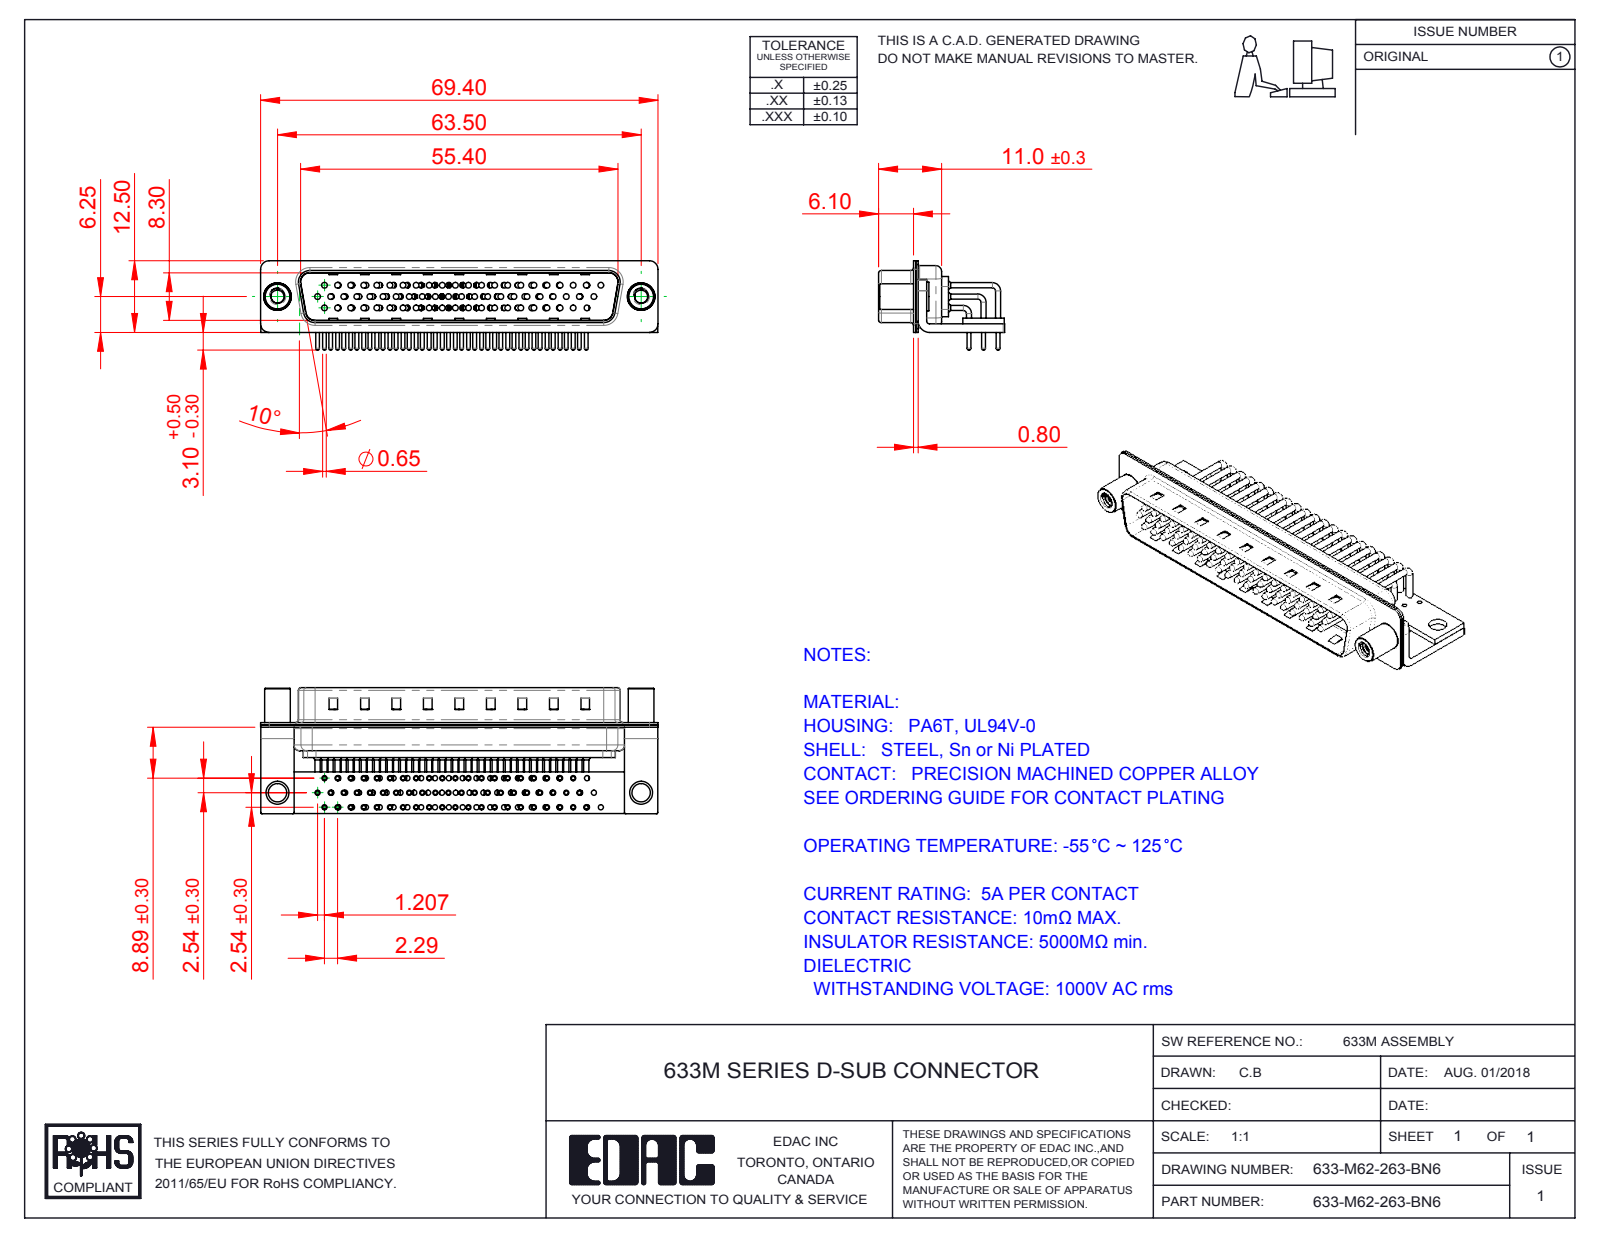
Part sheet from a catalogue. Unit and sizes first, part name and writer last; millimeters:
Units: millimetres
Overall size (bounding box): 69.4 × 22 × 15.6
Round holes (diameter × count): ⌀0.9 ×62, ⌀1 ×62, ⌀1.7 ×62, ⌀2 ×62, ⌀2.26 ×2, ⌀3.2 ×2, ⌀4 ×2, ⌀4.8 ×2
Round bosses / shafts (diameter × count): ⌀0.9 ×118, ⌀1.5 ×62, ⌀0.65 ×62, ⌀1 ×56, ⌀5 ×2, ⌀4.9 ×2, ⌀4.5 ×2
Partial cylindrical surfaces — rounded edges, fillets, slot ends (radius × count): R1.01 ×62, R0.25 ×16, R1.5 ×16, R2 ×13, R0.5 ×9, R1.6 ×8, R0.6 ×4, R0.65 ×4
Main face-to-face distances: 0.4, 0.85, 1.25, 1.5, 9.55, 1, 1.9, 10.4, 8.3, 0.8
Hole centre spacings: 7.24, 2.41, 9.65, 4.83, 14.48, 16.89, 2.81, 2.32
Volume: 5 201 mm³ · Surface area: 15 819 mm²
Bodies: 70 solids, 7456 faces (4199 planar, 2561 cylindrical, 696 other)
Part name (STEP PRODUCT): 633M Contact Row 1; 633M Shell Front_62 Contacts; 633-M62-263-BN6; 633M Shell Rear_62 Contacts (+6 more)
STEP written by: SolidWorks 2016 (CONFIG_CONTROL_DESIGN)
